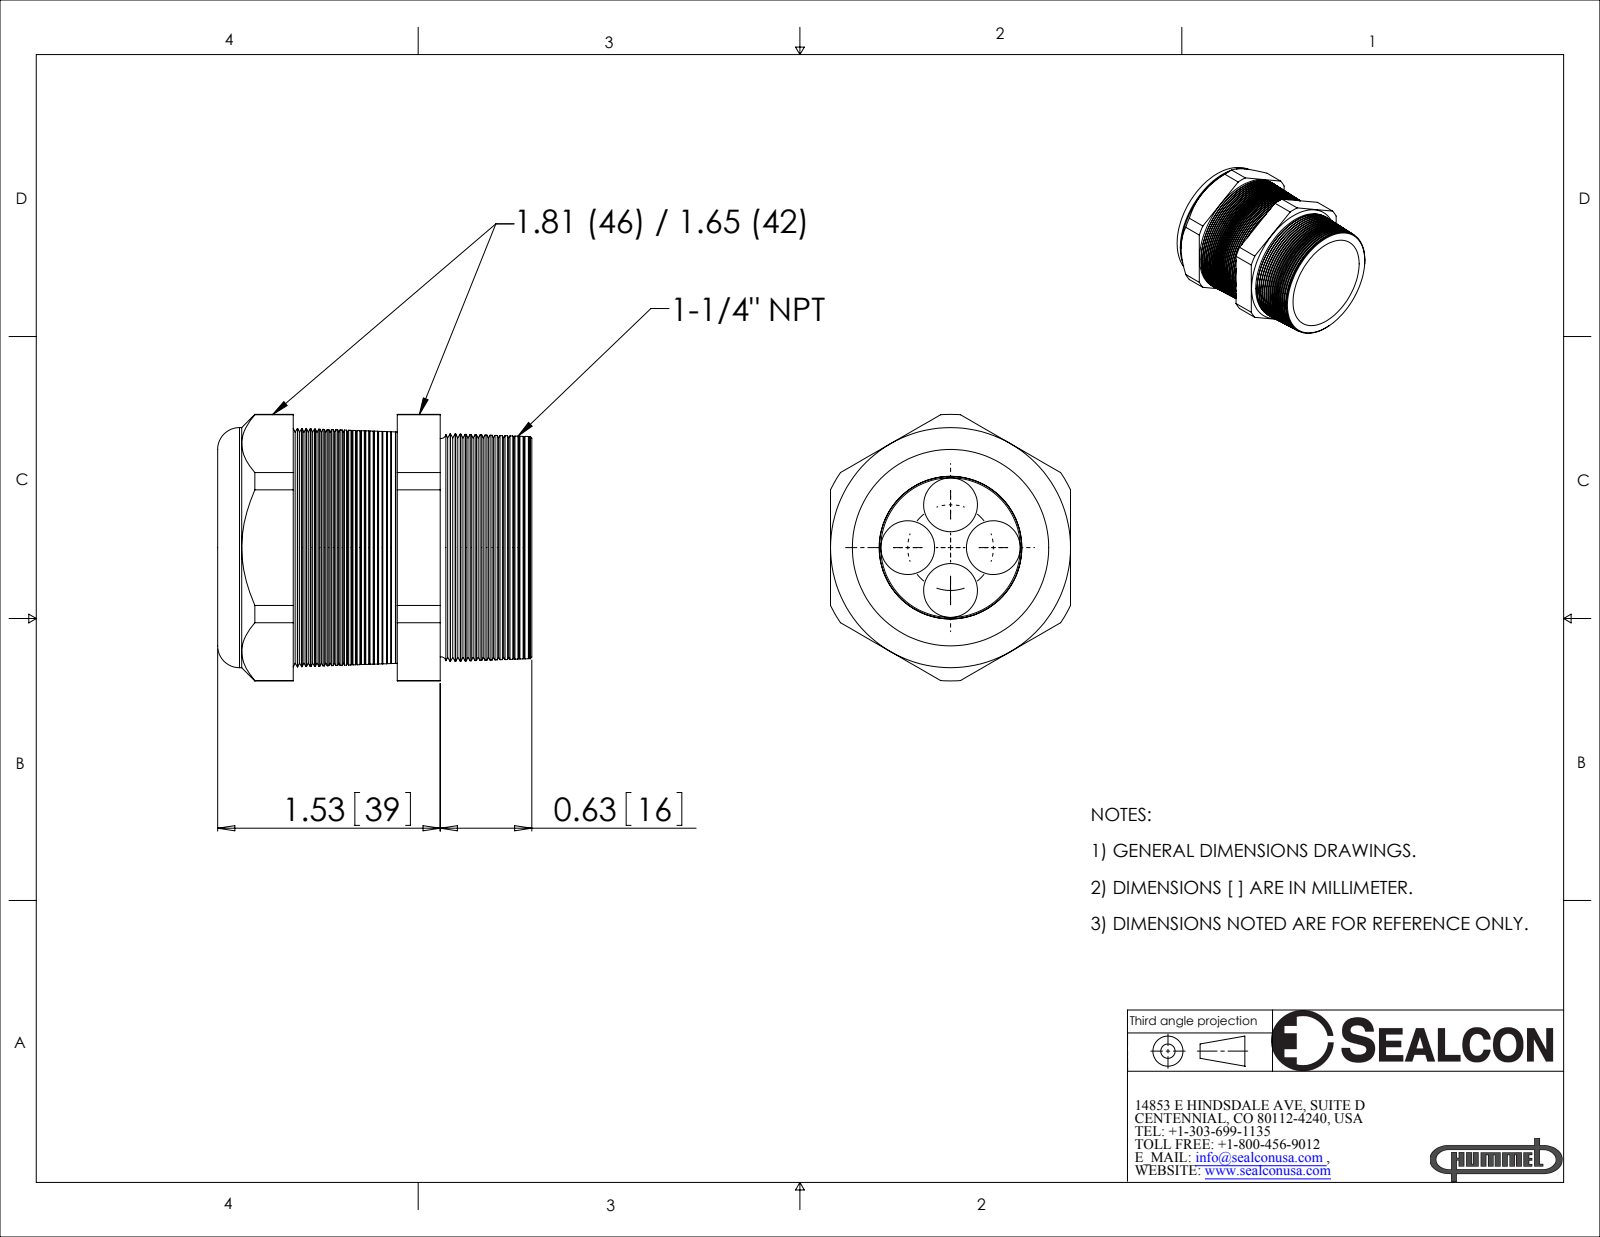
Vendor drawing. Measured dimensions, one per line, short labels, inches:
name: CD29L3-GY
written by: SolidWorks 2007 (CONFIG_CONTROL_DESIGN)
unit: in
bodies: 2 solids, 315 faces (21 planar, 28 cylindrical, 266 other)
size: 2.16 × 1.831 × 1.65
volume: 2.548 in³; area: 29.67 in²
holes: 4× ⌀0.37, 1× ⌀0.96, 1× ⌀0.98
bosses: 1× ⌀1.65
rounds: 1× R0.916
face distances: 1.65, 1.65, 2.16, 1.235, 0.925, 0.5, 0.735, 1.66, 0.02, 0.48
hole spacings: 0.294, 0.416, 0.588
